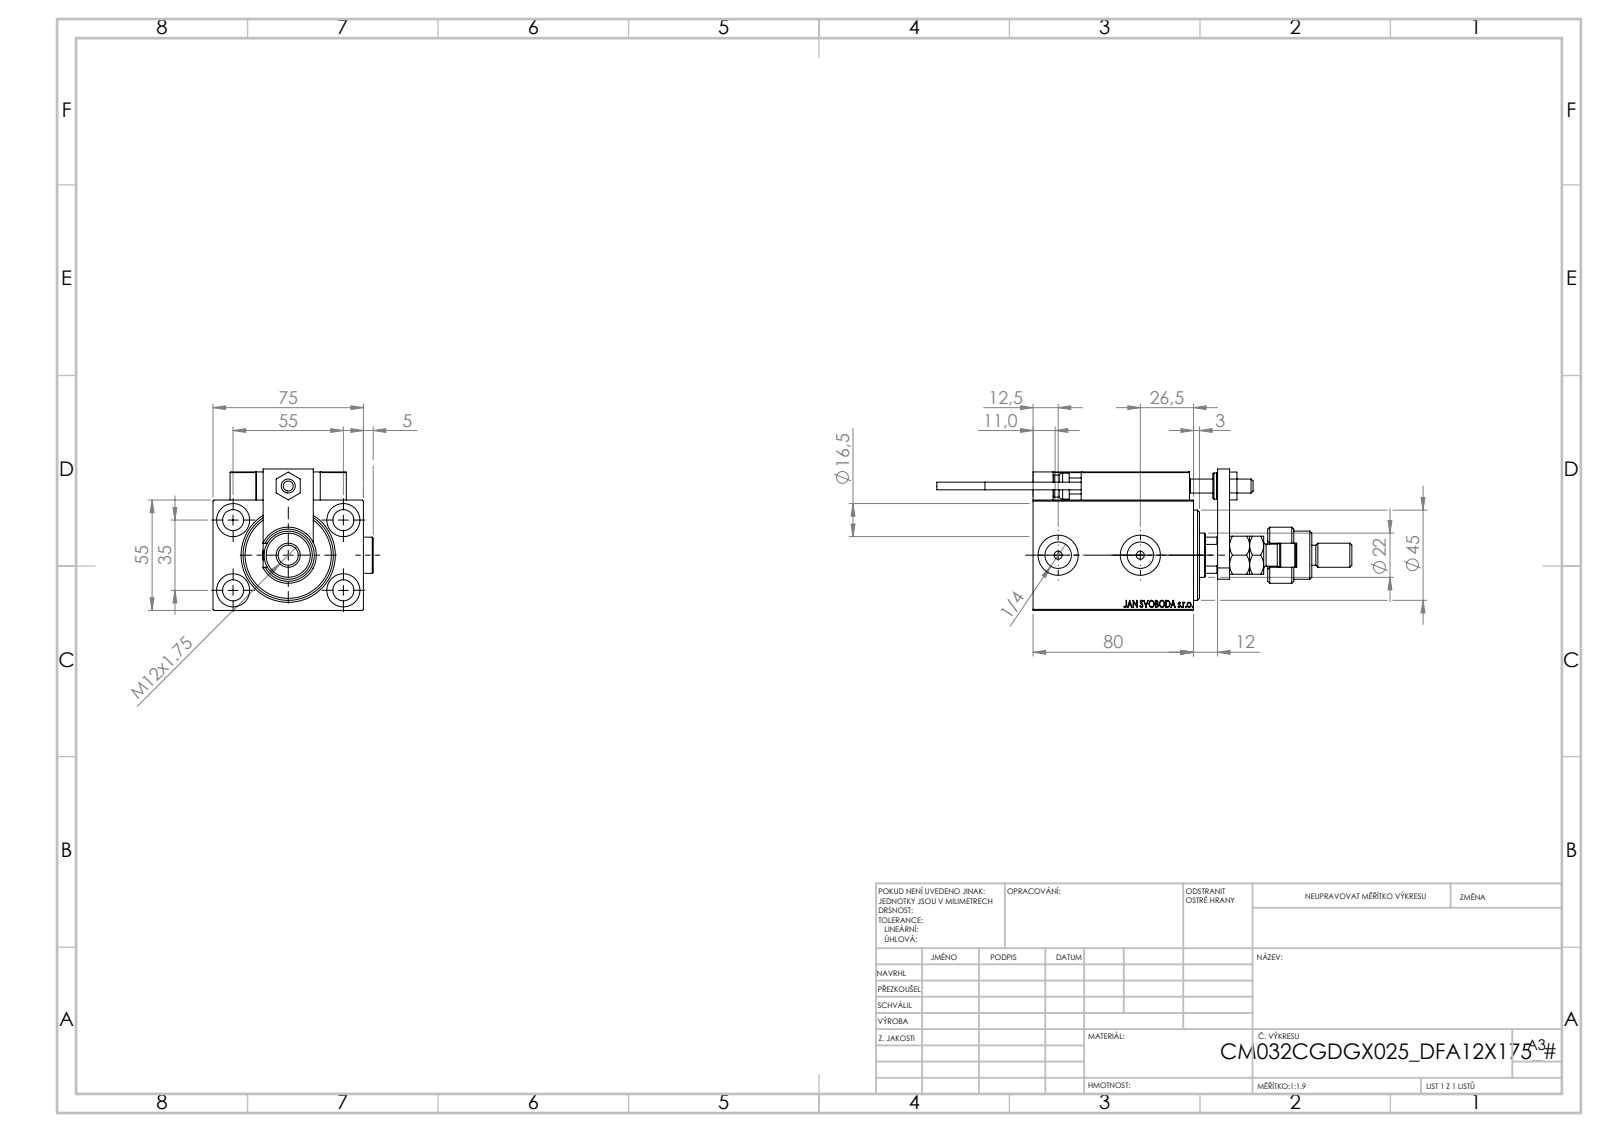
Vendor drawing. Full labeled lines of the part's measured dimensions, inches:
Part name (STEP PRODUCT): V450CM_C_Body; KONCOVKA; SWITCH X; Zatka_OIL_PORT (+7 more)
STEP written by: SolidWorks 2019 (CONFIG_CONTROL_DESIGN)
Units: inches
Bodies: 27 solids, 1421 faces (622 planar, 217 cylindrical, 582 other)
Overall size (bounding box): 8.15 × 3.146 × 2.776
Volume: 21.15 in³ · Surface area: 151.1 in²
Round holes (diameter × count): ⌀0.157 ×6, ⌀0.315 ×5, ⌀0.413 ×5, ⌀0.65 ×5, ⌀0.126 ×4, ⌀0.197 ×2, ⌀0.518 ×2, ⌀0.787 ×2, ⌀0.276 ×1, ⌀0.866 ×1, ⌀1.004 ×1, ⌀1.26 ×1
Round bosses / shafts (diameter × count): ⌀0.709 ×3, ⌀0.433 ×2, ⌀0.197 ×2, ⌀0.15 ×2, ⌀1.102 ×1, ⌀0.945 ×1, ⌀0.512 ×1, ⌀0.472 ×1
Partial cylindrical surfaces — rounded edges, fillets, slot ends (radius × count): R0.012 ×30, R0.118 ×2, R0.384 ×1, R0.413 ×1
Main face-to-face distances: 2.165, 2.953, 0.551, 2.717, 0.472, 0.394, 0.984, 0.709, 2.283, 0.197
Hole centre spacings: 1.283, 0.448, 0.787, 1.165, 1.169, 1.262, 1.273, 1.378
